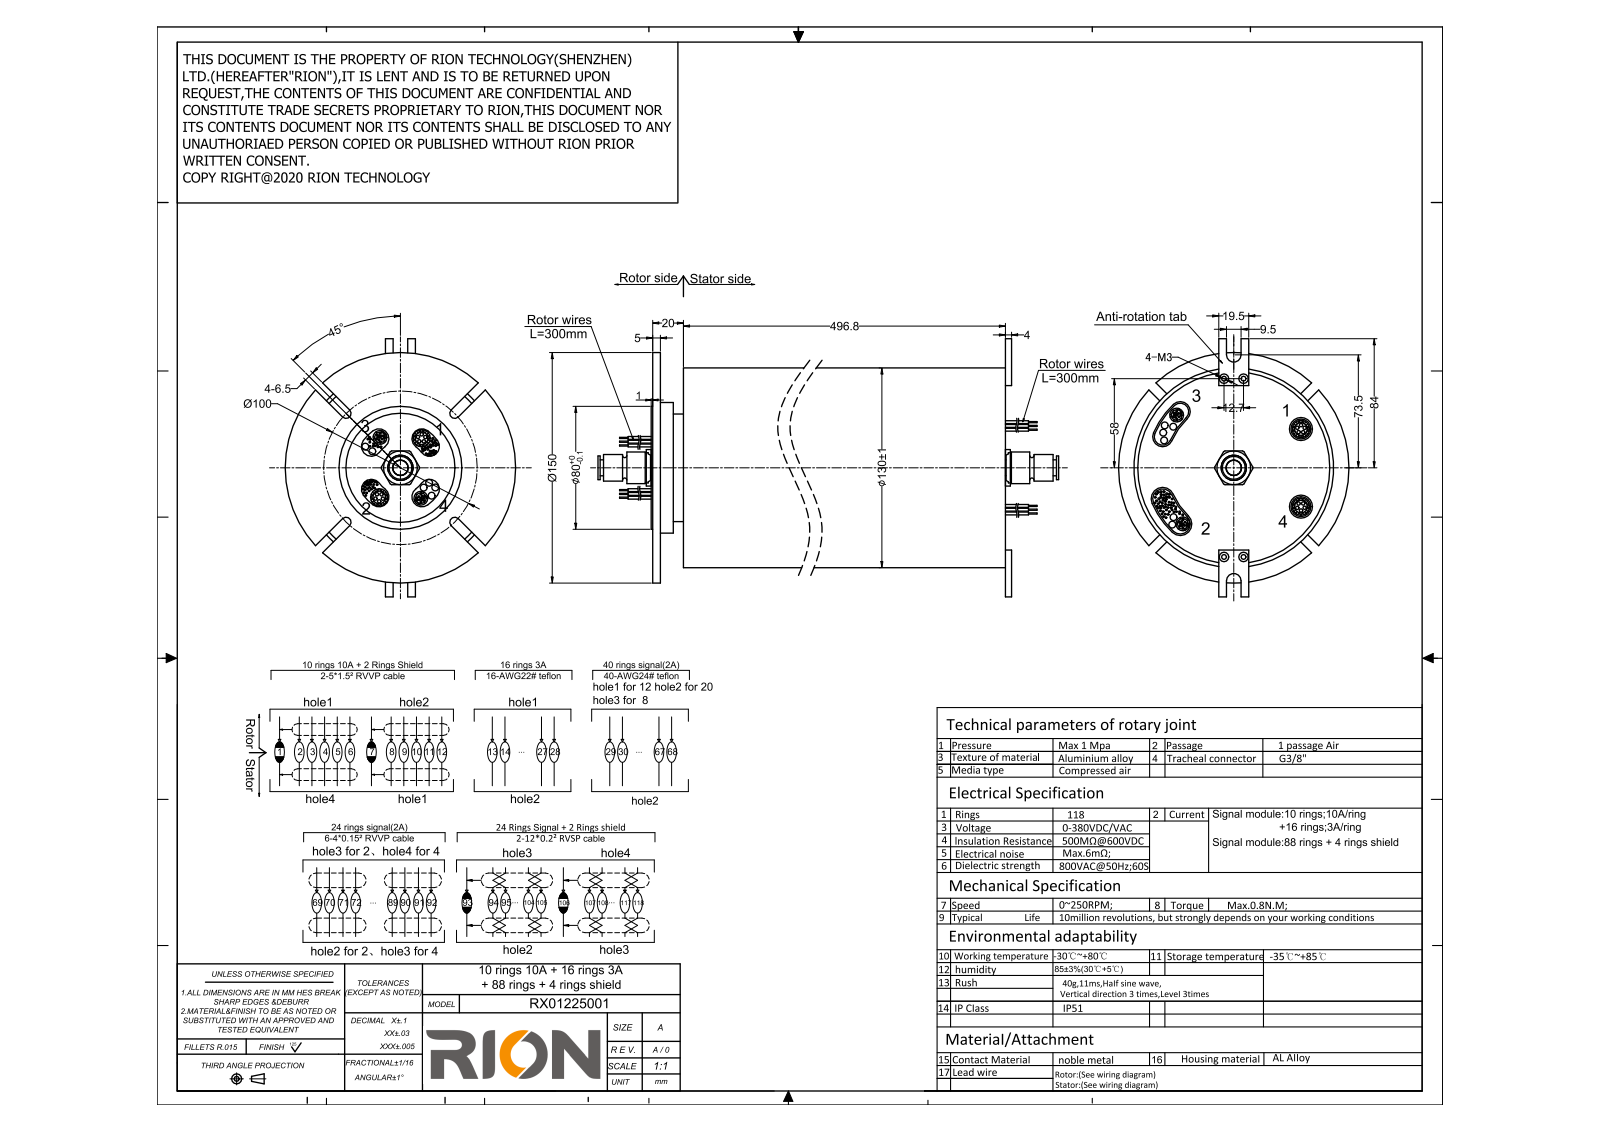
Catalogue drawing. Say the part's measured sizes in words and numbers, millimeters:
The part is named "RX01225001; KSH12-03S; KQ2S12-03S". Its 3-D file was written by "SolidWorks 2014 (CONFIG_CONTROL_DESIGN)". It is 3 solids with 632 faces: 219 planar, 383 cylindrical and 30 other. Overall it measures 582.8 by 168 by 150 millimeters. Its volume is 6 794 000 cubic millimeters and its surface area 296 849 square millimeters. Round holes: 4 of diameter 3.2, 3 of diameter 13, 1 of diameter 9, 1 of diameter 15.25, 1 of diameter 125. Round bosses or shafts: 90 of diameter 1.1, 32 of diameter 1.3, 12 of diameter 4.5, 4 of diameter 11.3, 4 of diameter 9, 1 of diameter 150, 1 of diameter 130, 1 of diameter 124.4. Partial cylindrical surfaces (rounded edges, fillets, slot ends): 10 of radius 6.5, 4 of radius 3.25, 2 of radius 4.75, 2 of radius 5.5, 1 of radius 17, 1 of radius 30, 1 of radius 44, 1 of radius 45. The main face-to-face distances are 516.8, 5, 511.8, 20, 15, 496.8, 21, 1, 6, 517.8. The hole center spacings are 58.35, 50.5, 12.7, 49.7, 59.84, 91.26, 97.15, 116.
